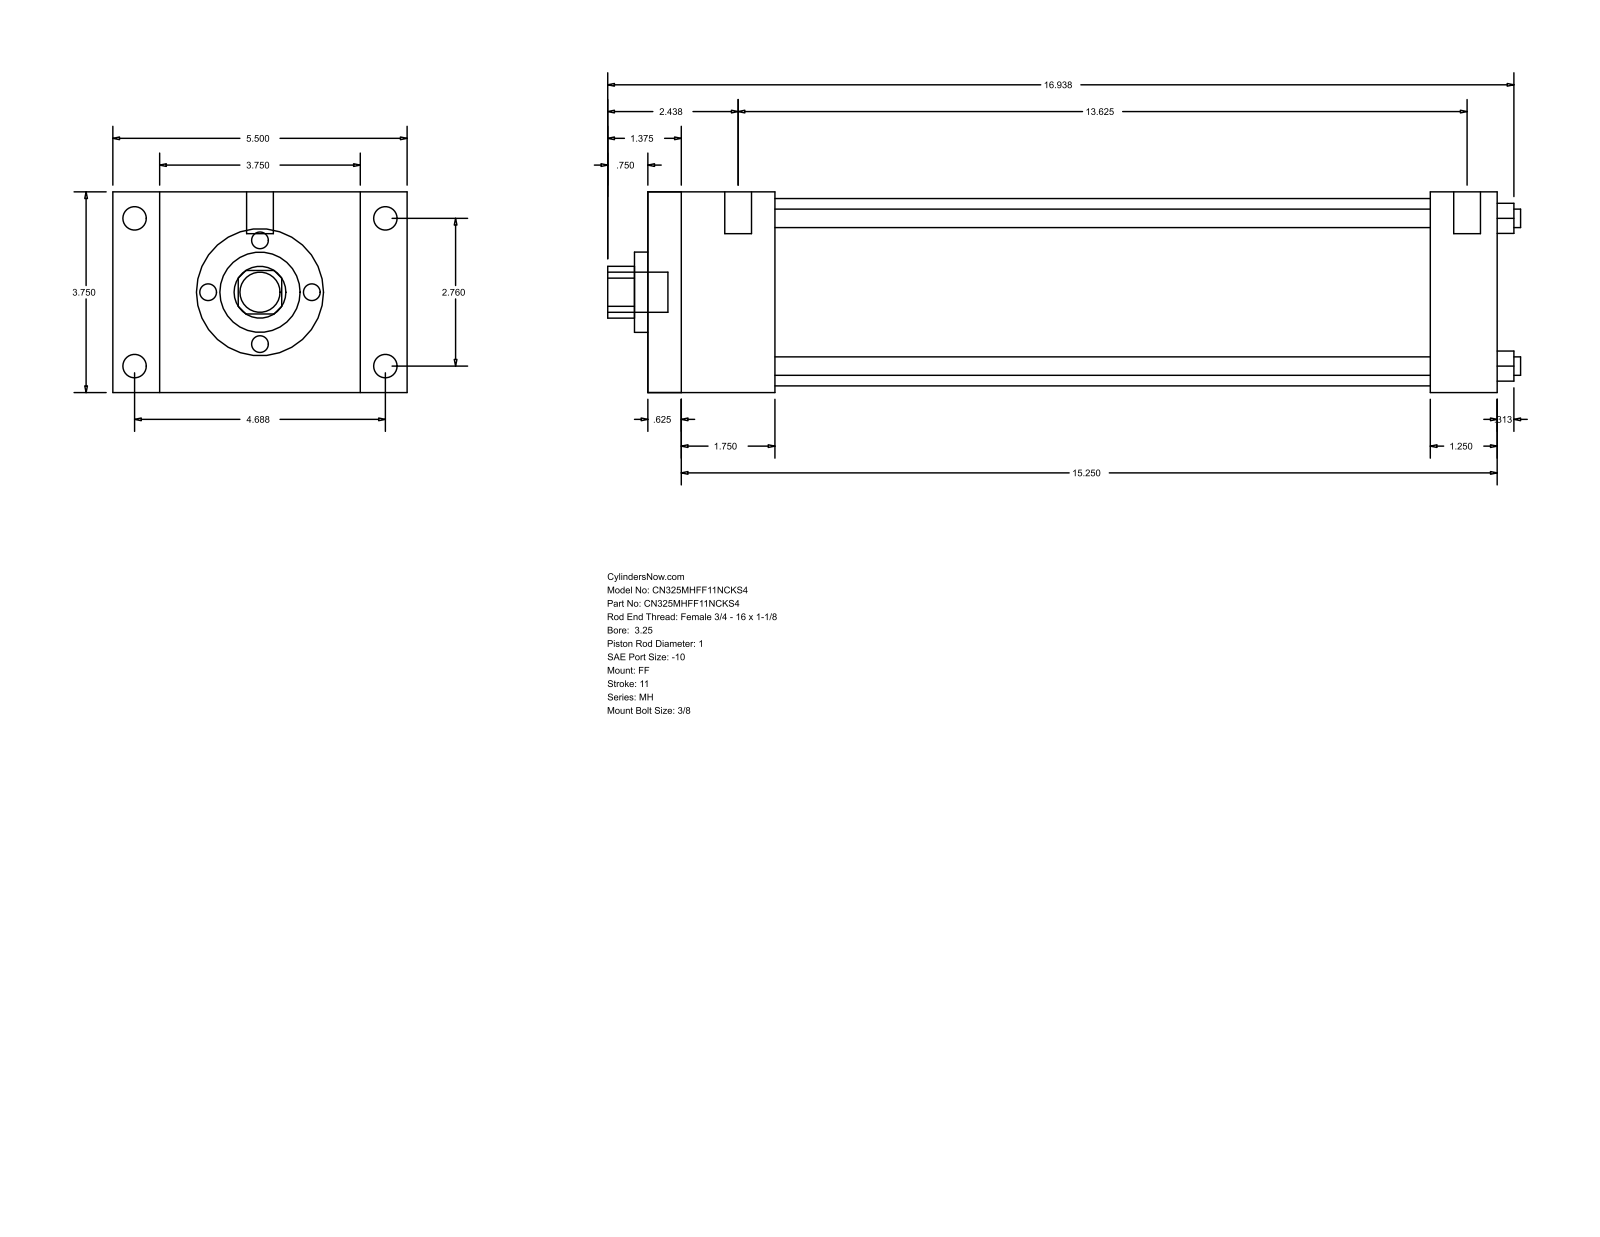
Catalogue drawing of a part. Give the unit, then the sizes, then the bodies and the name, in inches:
Units: inches
Overall size (bounding box): 17.063 × 5.5 × 3.75
Round holes (diameter × count): ⌀0.345 ×4, ⌀1 ×1, ⌀1.5 ×1, ⌀3.5 ×1
Round bosses / shafts (diameter × count): ⌀0.438 ×4, ⌀0.219 ×4, ⌀0.5 ×2, ⌀0.75 ×1
Partial cylindrical surfaces — rounded edges, fillets, slot ends (radius × count): R0.484 ×1
Main face-to-face distances: 3.75, 15.875, 0.625, 15.25, 0.875, 4.625, 14.625, 14, 1.25, 2.375
Hole centre spacings: 1.952, 2.76, 3.903
Bodies: 0 solids, 92 faces (64 planar, 28 cylindrical, 0 other)
Part name (STEP PRODUCT): MH_FF__0325_1
STEP written by: GSSL Pune (CONFIG_CONTROL_DESIGN)
